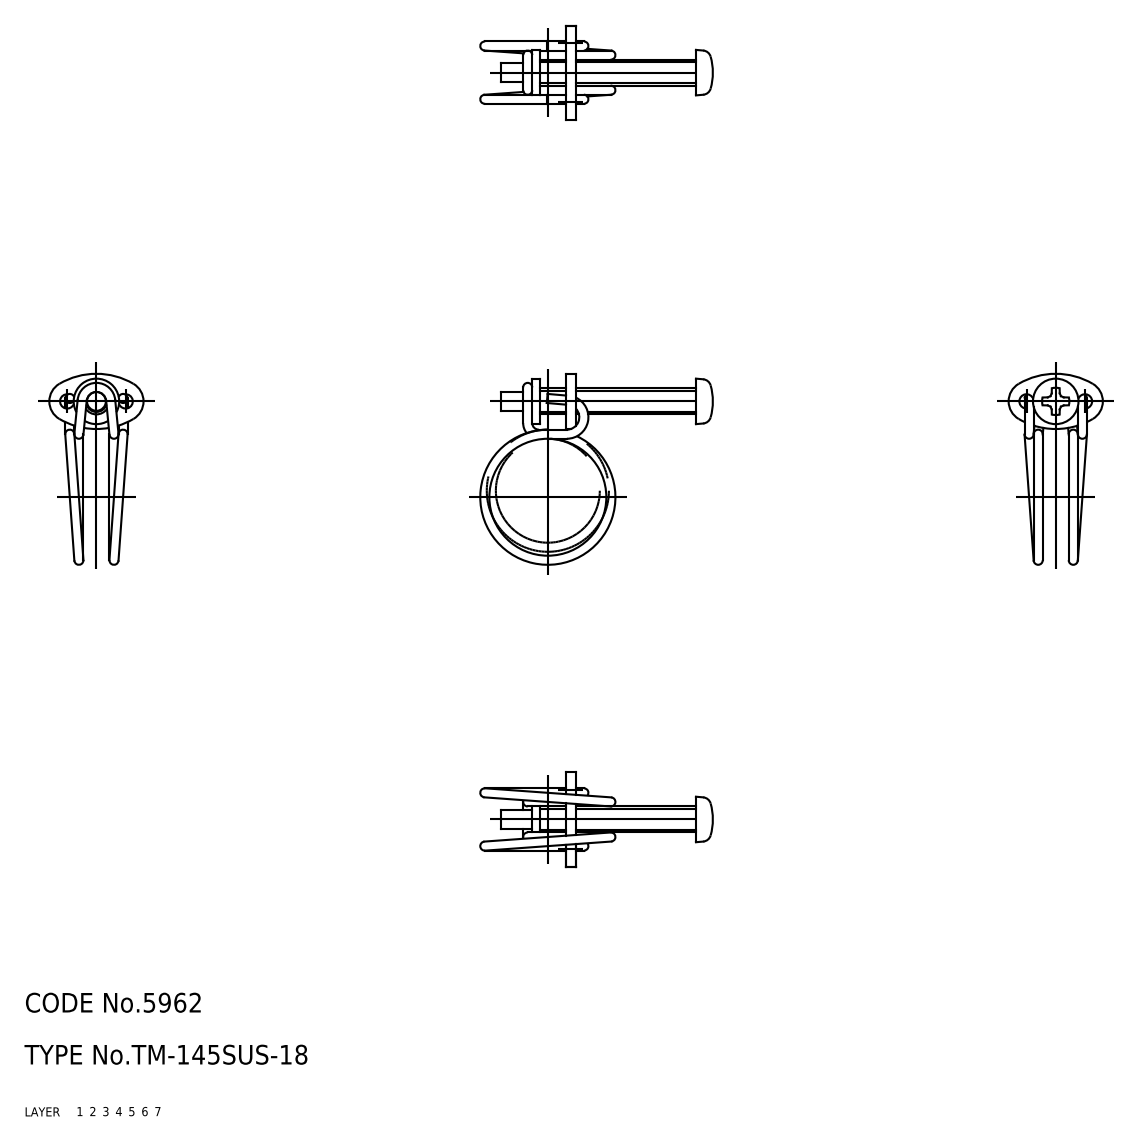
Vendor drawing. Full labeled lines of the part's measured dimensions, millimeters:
Part name (STEP PRODUCT): 67115124; 67115137; 67115150
STEP written by: CADfix (AUTOMOTIVE_DESIGN)
Units: millimetres
Bodies: 3 solids, 86 faces (0 planar, 0 cylindrical, 86 other)
Overall size (bounding box): 35.73 × 29.4 × 14.5
Volume: 836 mm³ · Surface area: 1 553 mm²
